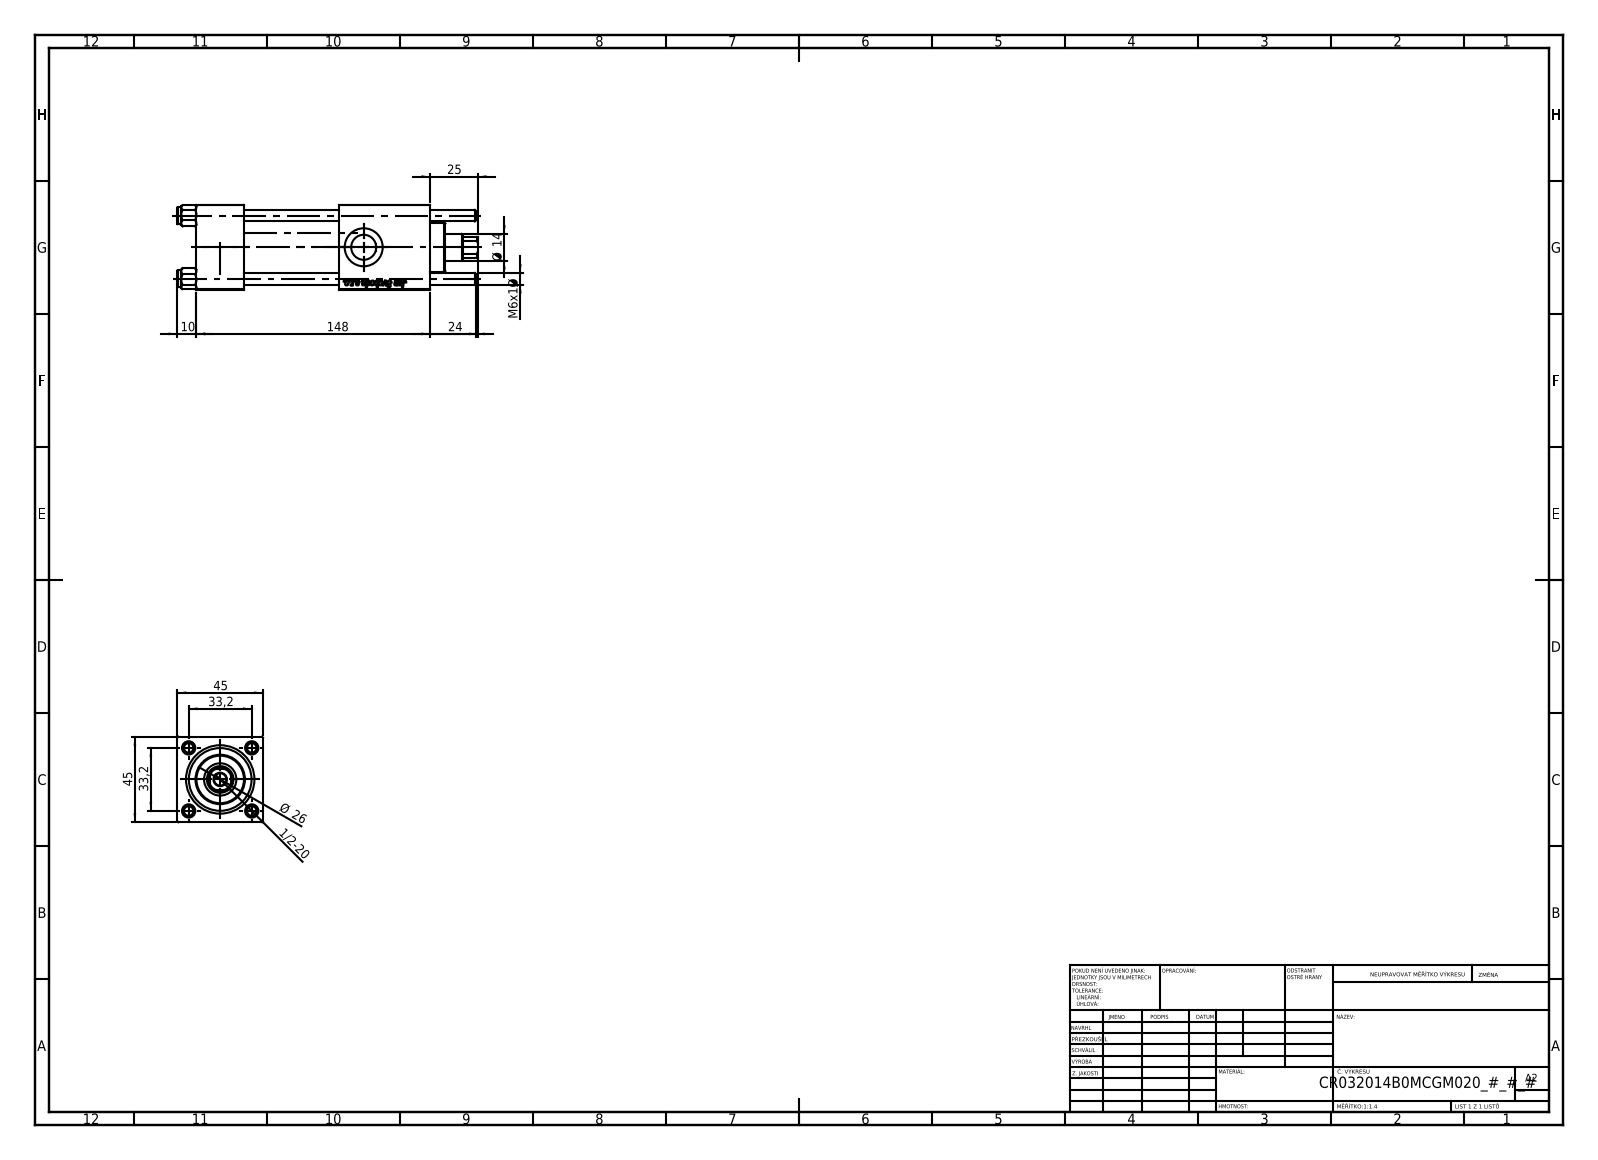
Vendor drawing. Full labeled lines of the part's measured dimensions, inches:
Part name (STEP PRODUCT): V215CR_VCP_B; V215_VC_A; V215CR_B-1; NUT_M5_B (+1 more)
STEP written by: SolidWorks 2019 (CONFIG_CONTROL_DESIGN)
Units: inches
Bodies: 11 solids, 1156 faces (429 planar, 79 cylindrical, 648 other)
Overall size (bounding box): 6.22 × 1.772 × 1.772
Volume: 12.1 in³ · Surface area: 112.5 in²
Round holes (diameter × count): ⌀0.236 ×4, ⌀0.276 ×2, ⌀0.518 ×2, ⌀0.787 ×2, ⌀0.256 ×1, ⌀0.551 ×1, ⌀0.669 ×1, ⌀0.945 ×1, ⌀1.26 ×1, ⌀1.299 ×1
Round bosses / shafts (diameter × count): ⌀0.354 ×4, ⌀1.496 ×1, ⌀1.024 ×1
Partial cylindrical surfaces — rounded edges, fillets, slot ends (radius × count): R0.256 ×1
Main face-to-face distances: 1.772, 0.984, 4.843, 3.858, 1.969, 2.953, 1.89, 3.713, 2.728, 0.76
Hole centre spacings: 0.924, 1.307, 1.848
